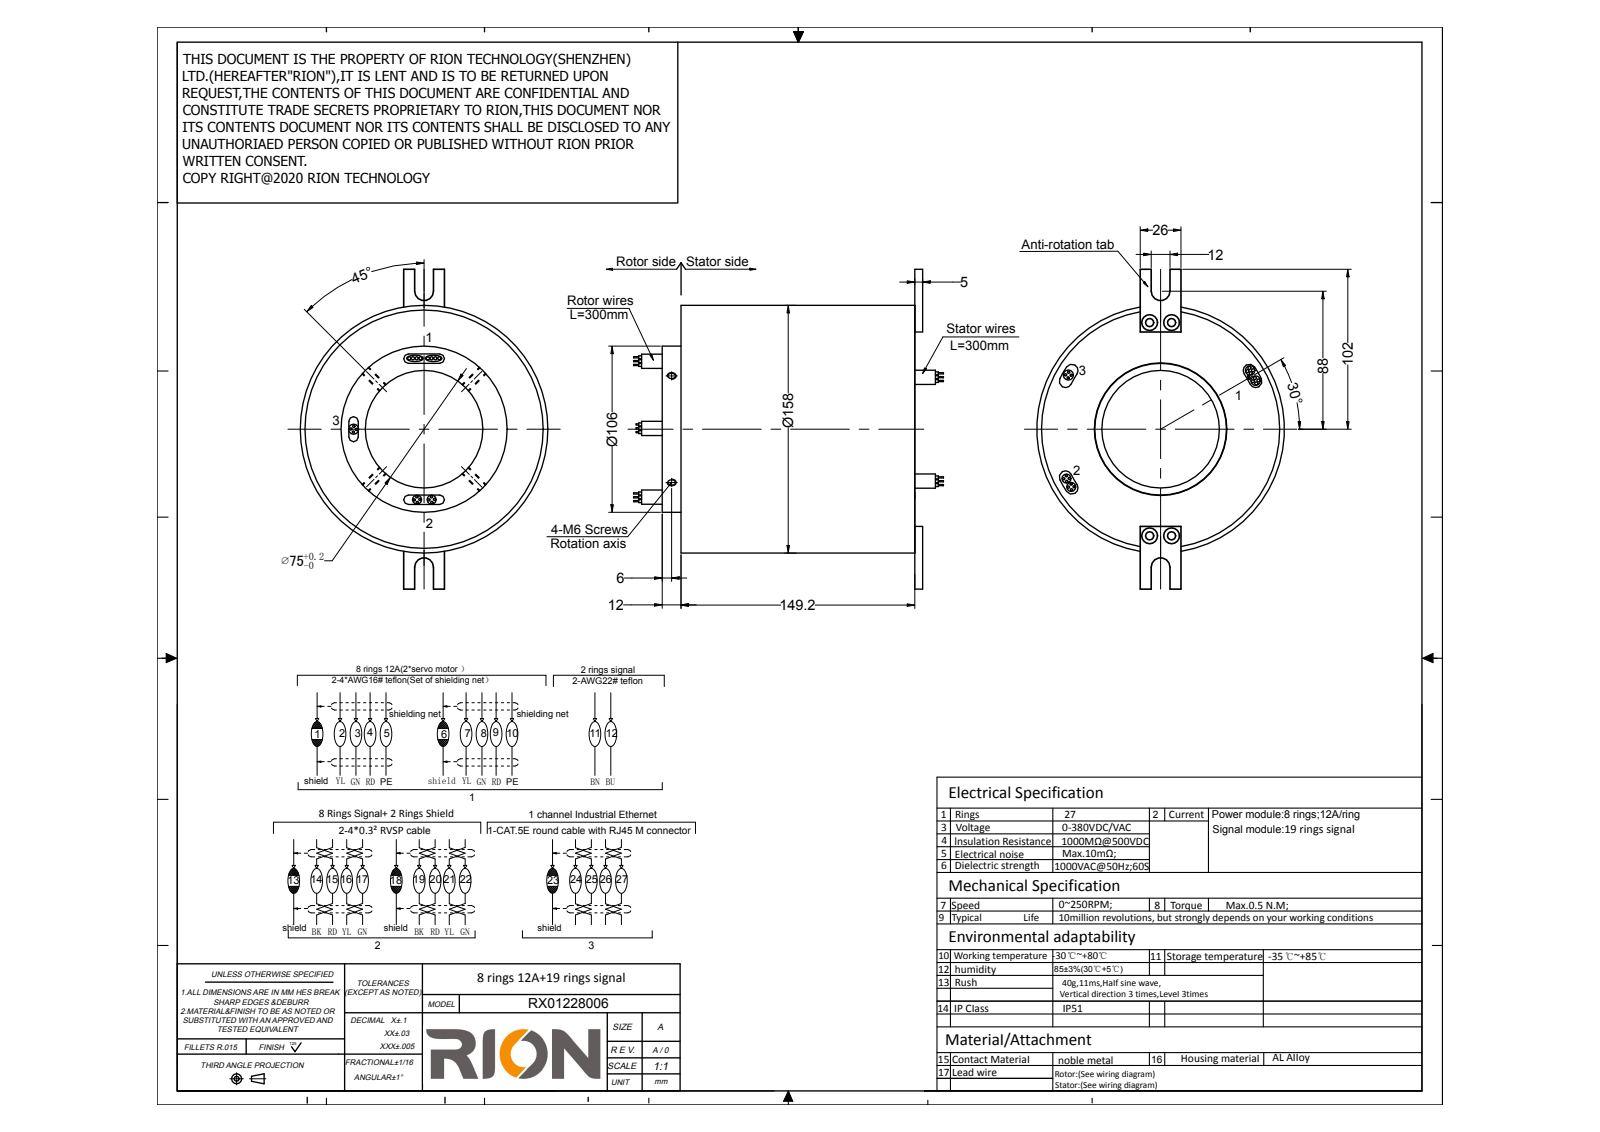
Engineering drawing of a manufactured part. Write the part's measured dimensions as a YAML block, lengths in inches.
step_written_by: "SolidWorks 2014 (CONFIG_CONTROL_DESIGN)"
units: inches
bodies: {solids: 1, faces: 181, planar: 72, cylindrical: 89, other: 20}
overall_size: [9.063, 8.031, 6.22]
volume: 142.4
surface_area: 258.5
round_holes:
  - {diameter: 0.197, count: 8}
  - {diameter: 0.165, count: 4}
  - {diameter: 2.953, count: 1}
  - {diameter: 3.701, count: 1}
  - {diameter: 5.984, count: 1}
round_bosses_or_shafts:
  - {diameter: 0.059, count: 4}
  - {diameter: 0.228, count: 3}
  - {diameter: 0.241, count: 2}
  - {diameter: 0.051, count: 2}
  - {diameter: 6.22, count: 1}
  - {diameter: 5.976, count: 1}
  - {diameter: 4.173, count: 1}
  - {diameter: 3.693, count: 1}
partial_cylinders:
  - {radius: 0.118, count: 6}
  - {radius: 0.157, count: 6}
  - {radius: 0.236, count: 2}
  - {radius: 0.128, count: 1}
face_to_face_distances: [5.874, 0.472, 6.346, 0.197, 6.543, 6.071, 0.039, 6.307, 1.024, 0.276]
hole_center_spacings: [2.691, 0.551, 5.354, 5.383]
